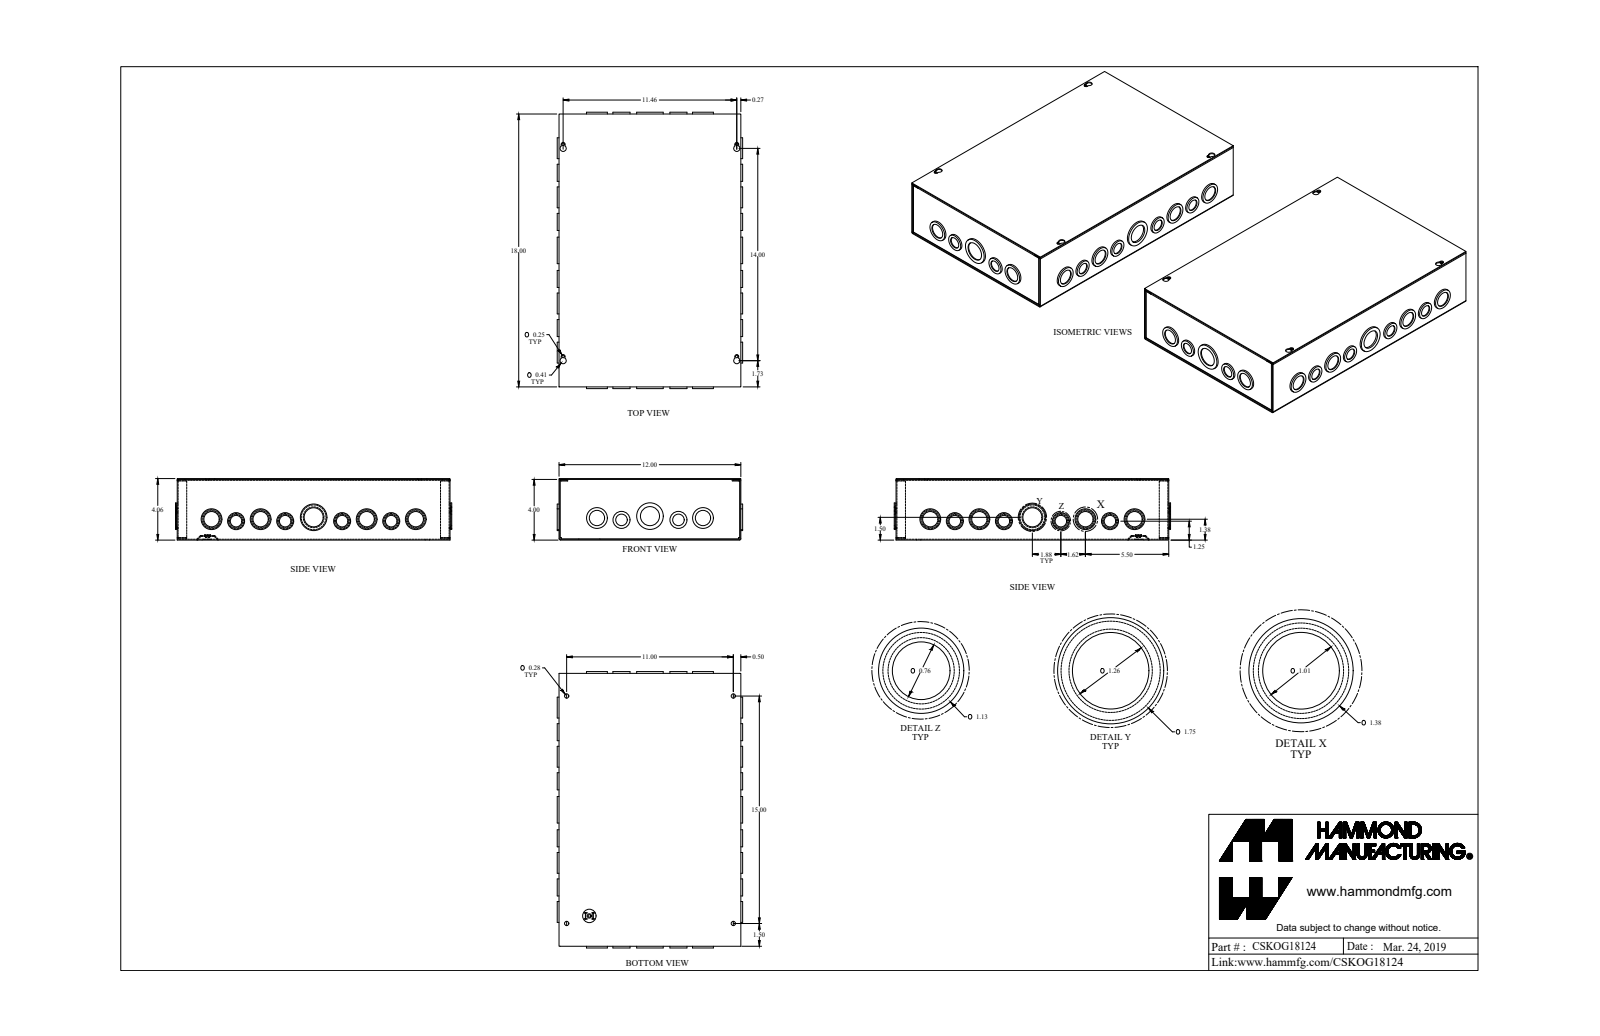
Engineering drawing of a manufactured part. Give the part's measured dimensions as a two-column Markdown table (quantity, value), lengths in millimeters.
| quantity | value |
| --- | --- |
| part name | CSKOG18124_Default |
| STEP written by | SolidWorks 2019 (CONFIG_CONTROL_DESIGN) |
| units | millimeters |
| bodies | 4 solids, 541 faces (237 planar, 296 cylindrical, 8 other) |
| overall size | 463.1 × 310.7 × 103 |
| volume | 680 900 mm³ |
| surface area | 949 000 mm² |
| round holes (diameter × count) | 25.7 × 12, 32 × 8, 19.3 × 6, 4.3 × 5, 7.1 × 4, 41.6 × 2, 12.7 × 1 |
| round bosses / shafts (diameter × count) | 28.6 × 10, 34.9 × 7, 22.2 × 6, 22.2 × 4, 34.9 × 3, 44.5 × 2, 28.6 × 2, 12.5 × 1 |
| partial cylindrical surfaces (radius × count) | 0.7 × 12, 2.2 × 12, 1.4 × 8, 3.2 × 4, 5.2 × 4 |
| main face-to-face distances | 1.4, 101.6, 100.2, 103, 303.4, 304.8, 455.8, 301.9, 457.2, 2.9 |
| hole center spacings | 41.3, 14, 48.2, 82.3, 89, 136.7, 177.8, 219 |
